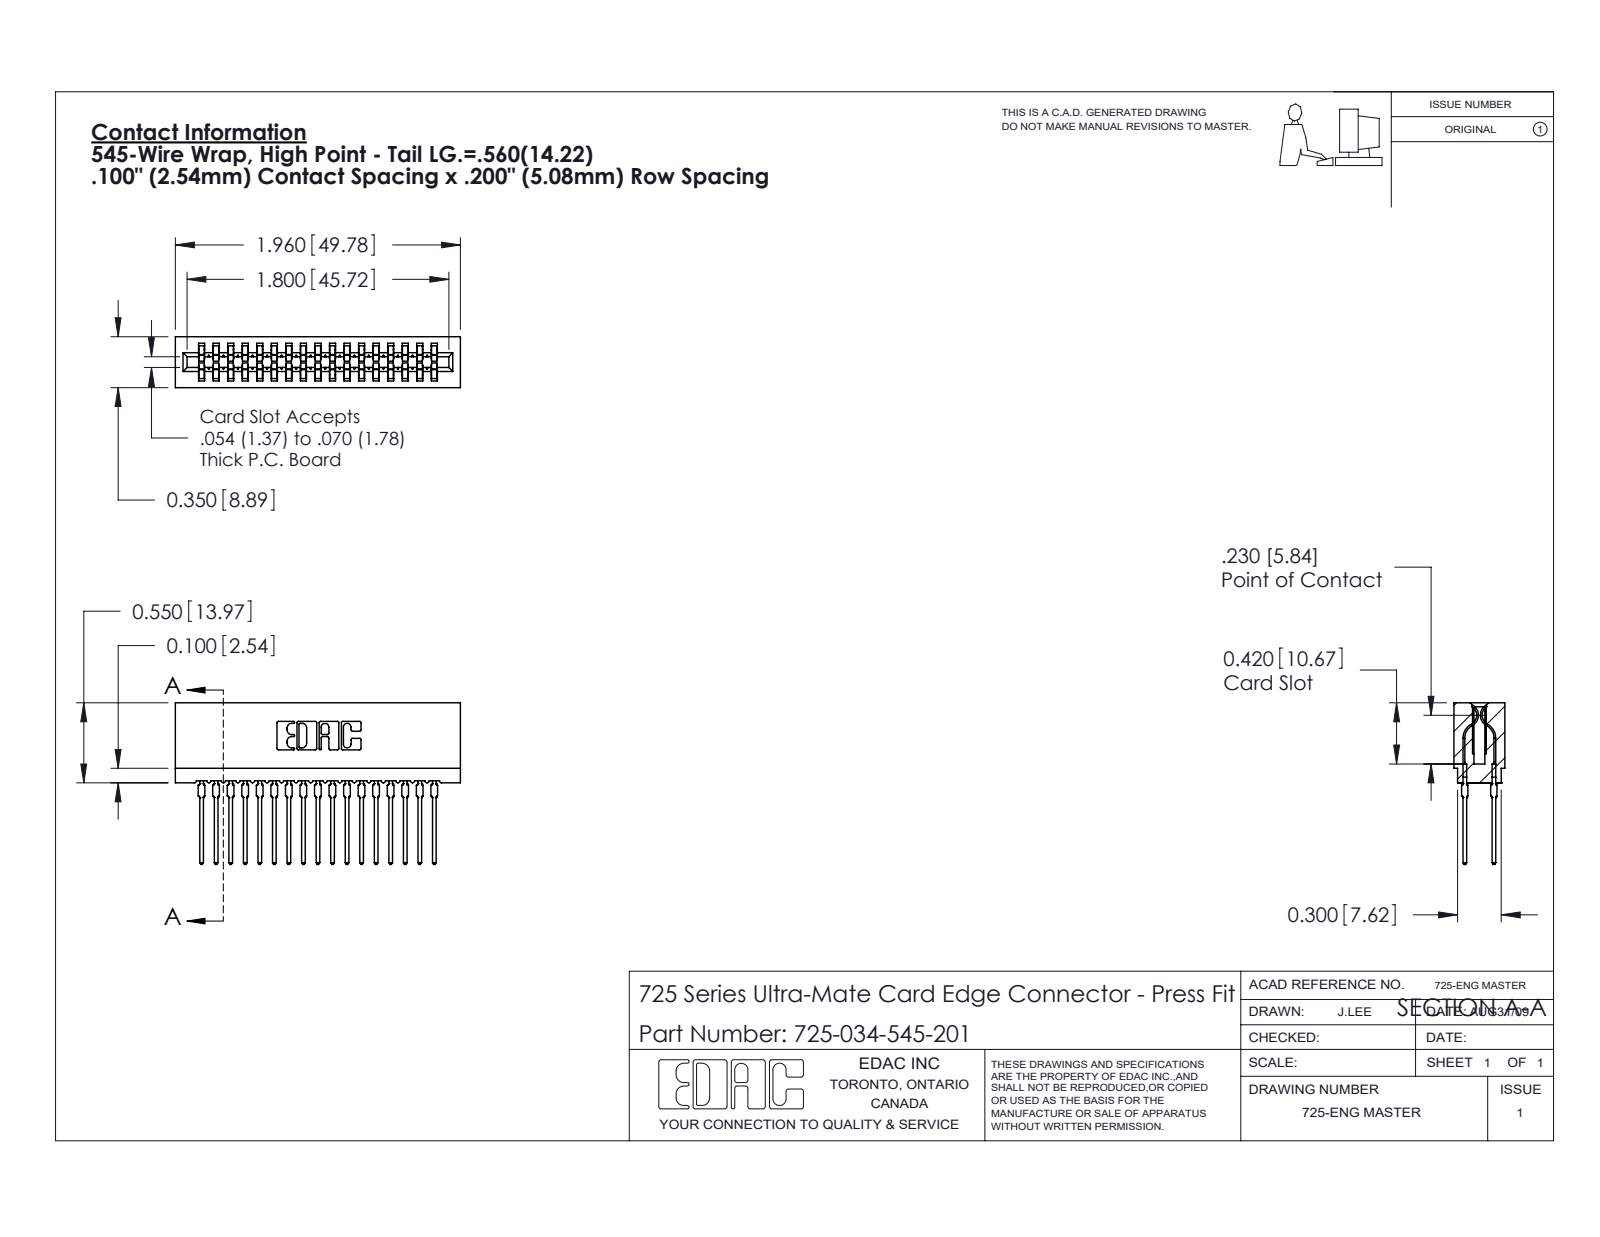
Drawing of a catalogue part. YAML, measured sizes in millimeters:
part_name: "725-034-545-201; 725 Part_Insulator Option - 01; 745-292-001_545"
step_written_by: "SolidWorks 2020 (CONFIG_CONTROL_DESIGN)"
units: millimeters
bodies: {solids: 35, faces: 3138, planar: 1619, cylindrical: 635, other: 884}
overall_size: [49.8, 28.2, 8.9]
volume: 4200
surface_area: 8839
partial_cylinders:
  - {radius: 0.5, count: 68}
  - {radius: 0.4, count: 34}
  - {radius: 0.3, count: 22}
  - {radius: 0.1, count: 8}
  - {radius: 0.3, count: 8}
  - {radius: 0.2, count: 6}
  - {radius: 0.8, count: 6}
  - {radius: 0.7, count: 3}
face_to_face_distances: [5.1, 2.5, 7.6, 1.6, 7.3, 10.2, 12.7, 15.2, 17.8, 8.9]
